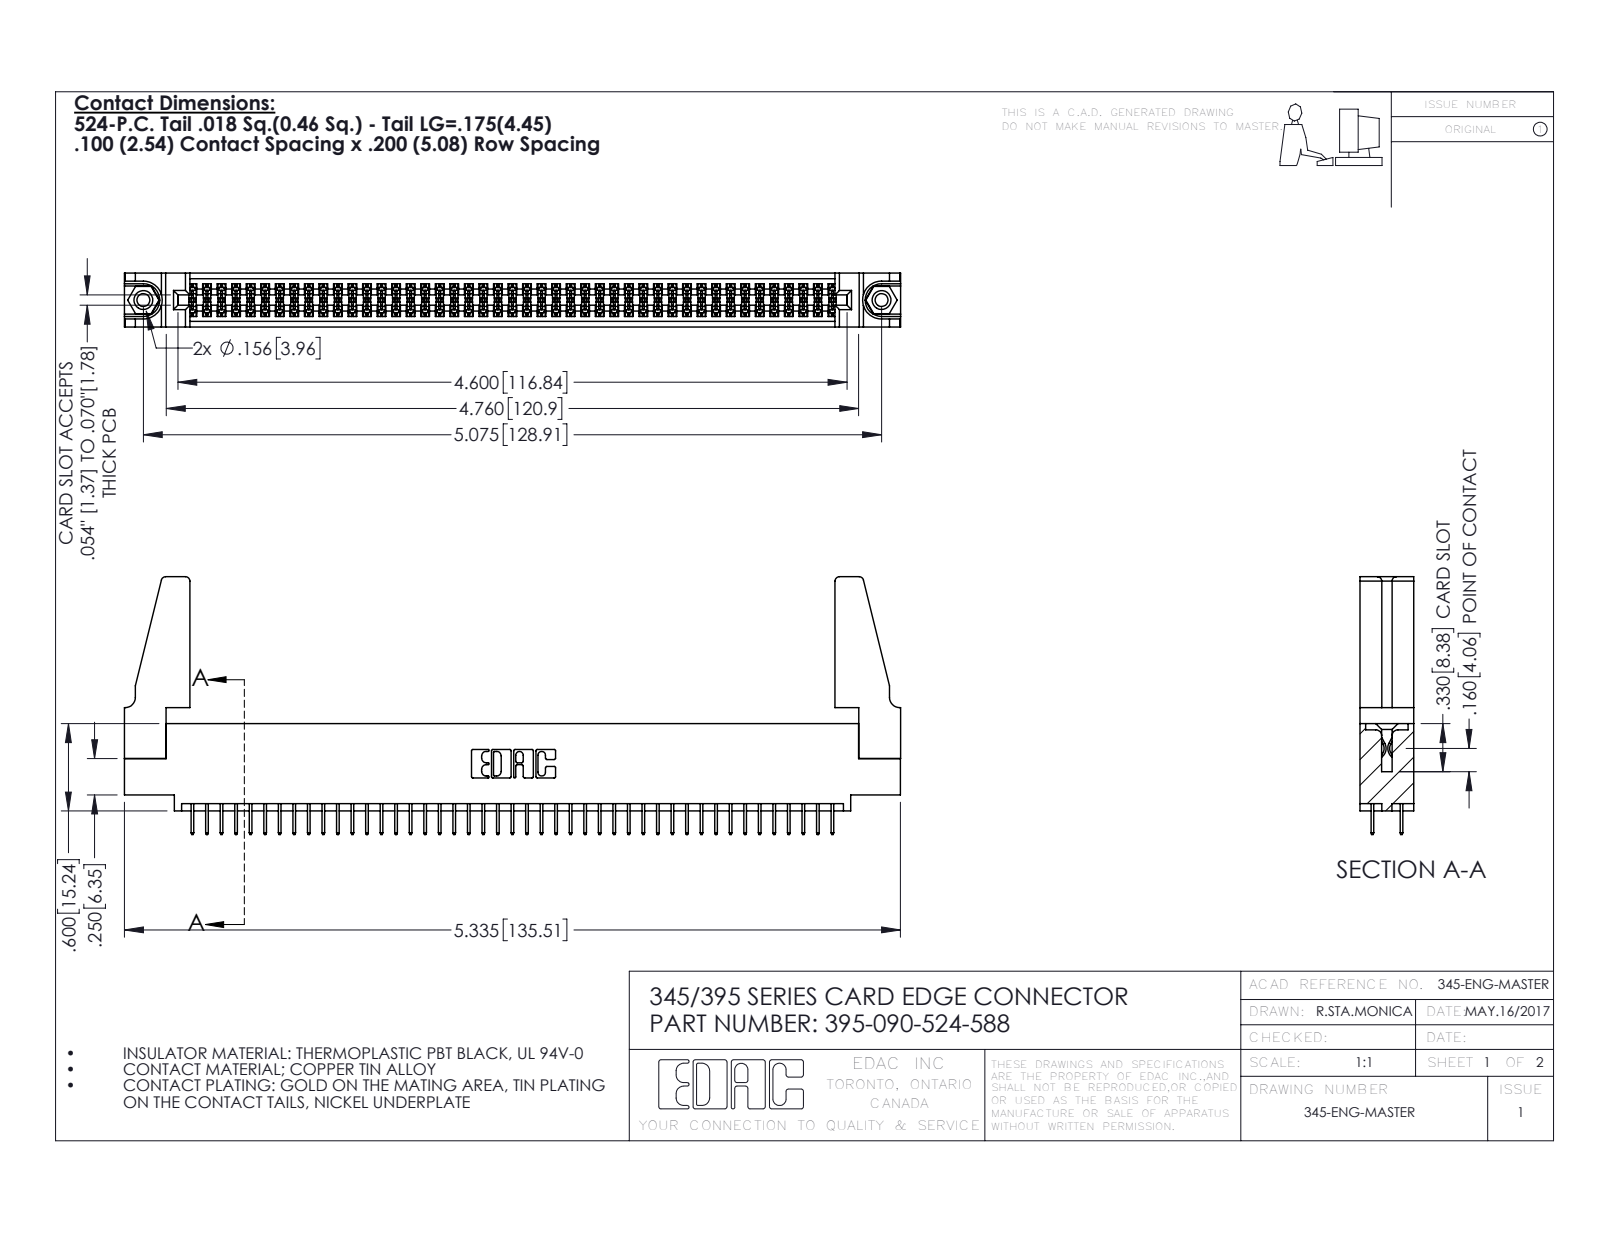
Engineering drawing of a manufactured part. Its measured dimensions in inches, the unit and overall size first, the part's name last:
Units: inches
Overall size (bounding box): 5.336 × 1.772 × 0.37
Round holes (diameter × count): ⌀0.089 ×2, ⌀0.125 ×2, ⌀0.156 ×2, ⌀0.064 ×1
Round bosses / shafts (diameter × count): ⌀0.155 ×2
Partial cylindrical surfaces — rounded edges, fillets, slot ends (radius × count): R0.006 ×135, R0.01 ×22, R0.03 ×8, R0.007 ×6, R0.031 ×6, R0.026 ×3, R0.014 ×2, R0.019 ×2
Main face-to-face distances: 0.072, 0.298, 0.37, 0.2, 0.098, 0.272, 0.025, 0.225, 0.072, 0.175
Hole centre spacings: 0.27, 4.839, 5.075
Volume: 0.991 in³ · Surface area: 34.26 in²
Bodies: 95 solids, 5114 faces (3666 planar, 1432 cylindrical, 16 other)
Part name (STEP PRODUCT): 395-090-524-588; 345-292-001_345-293-124; 345 Part_0.110 Offset - 0.156 Dia-TH; 345-250-001_345-250-001-102 (+1 more)
STEP written by: SolidWorks 2016 (CONFIG_CONTROL_DESIGN)
